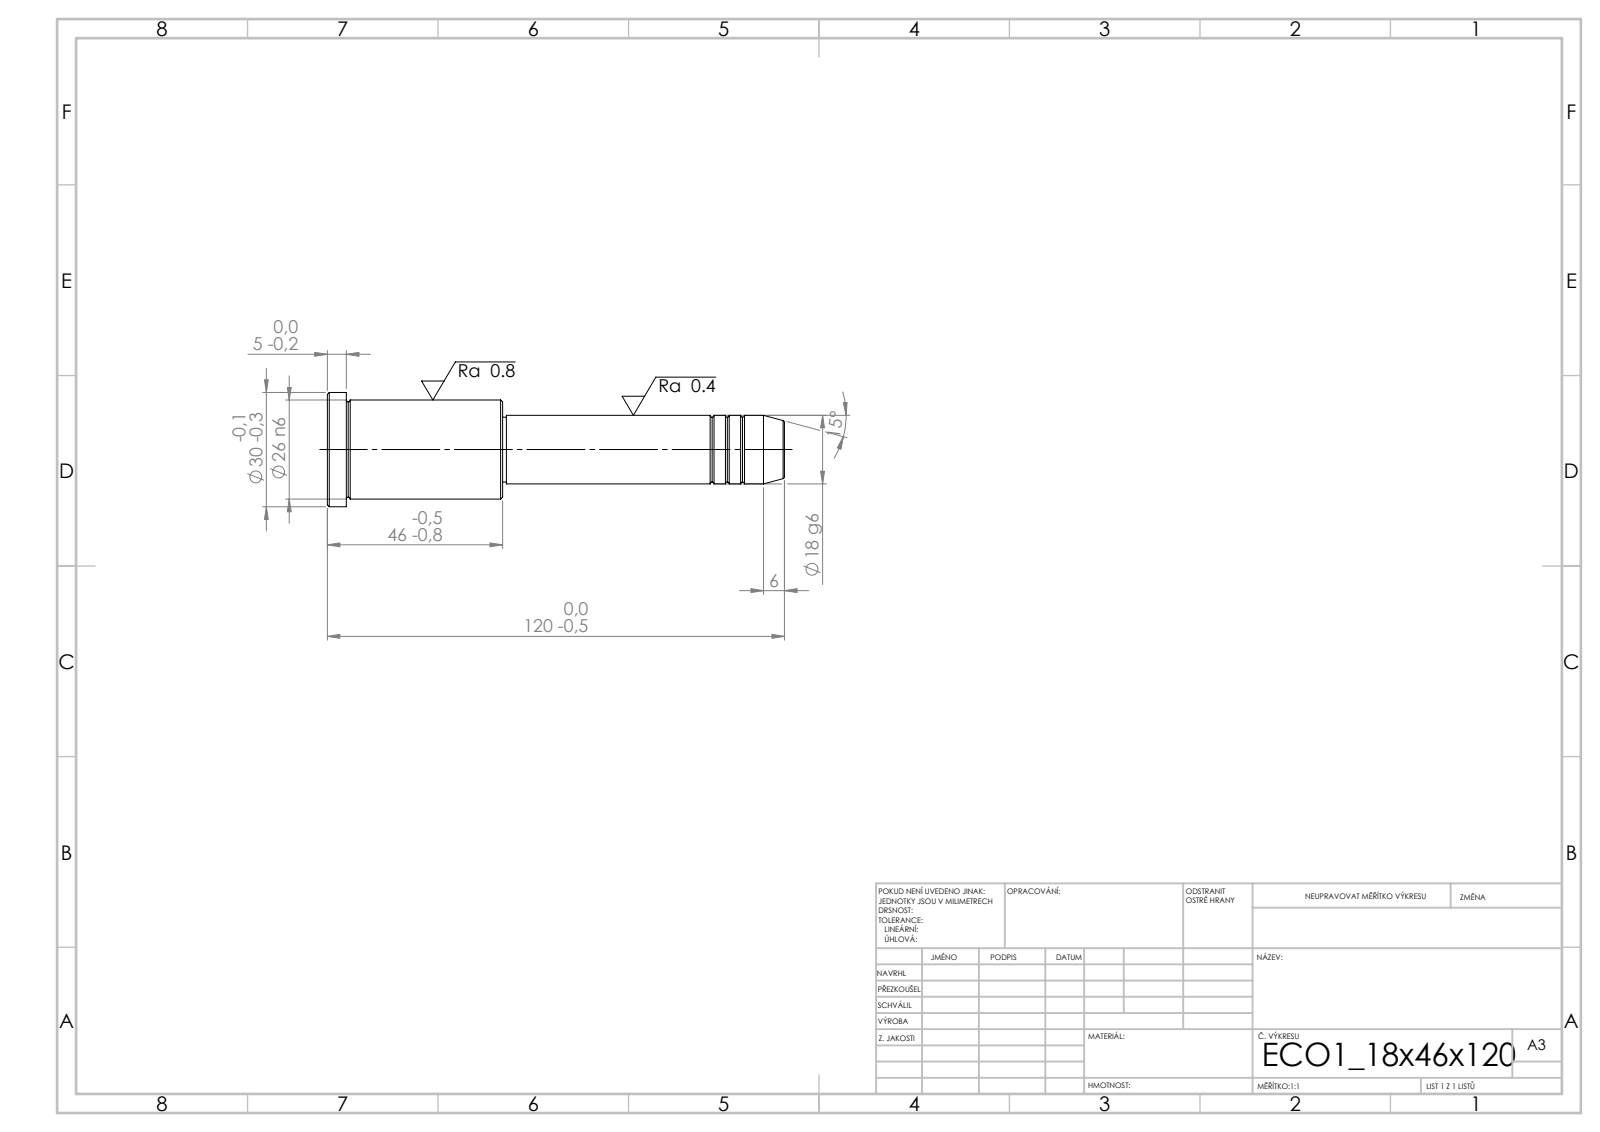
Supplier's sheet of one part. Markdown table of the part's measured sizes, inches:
| quantity | value |
| --- | --- |
| STEP written by | SolidWorks 2019 (CONFIG_CONTROL_DESIGN) |
| units | inches |
| bodies | 1 solid, 43 faces (5 planar, 14 cylindrical, 24 other) |
| overall size | 4.724 × 1.181 × 1.181 |
| volume | 2.671 in³ |
| surface area | 14.65 in² |
| round bosses / shafts (diameter × count) | 1.181 × 1, 1.024 × 1, 0.709 × 1, 0.669 × 1 |
| main face-to-face distances | 1.811, 1.614, 0.197, 2.913, 4.528, 4.724, 2.874, 0.039, 1.654, 1.85 |
